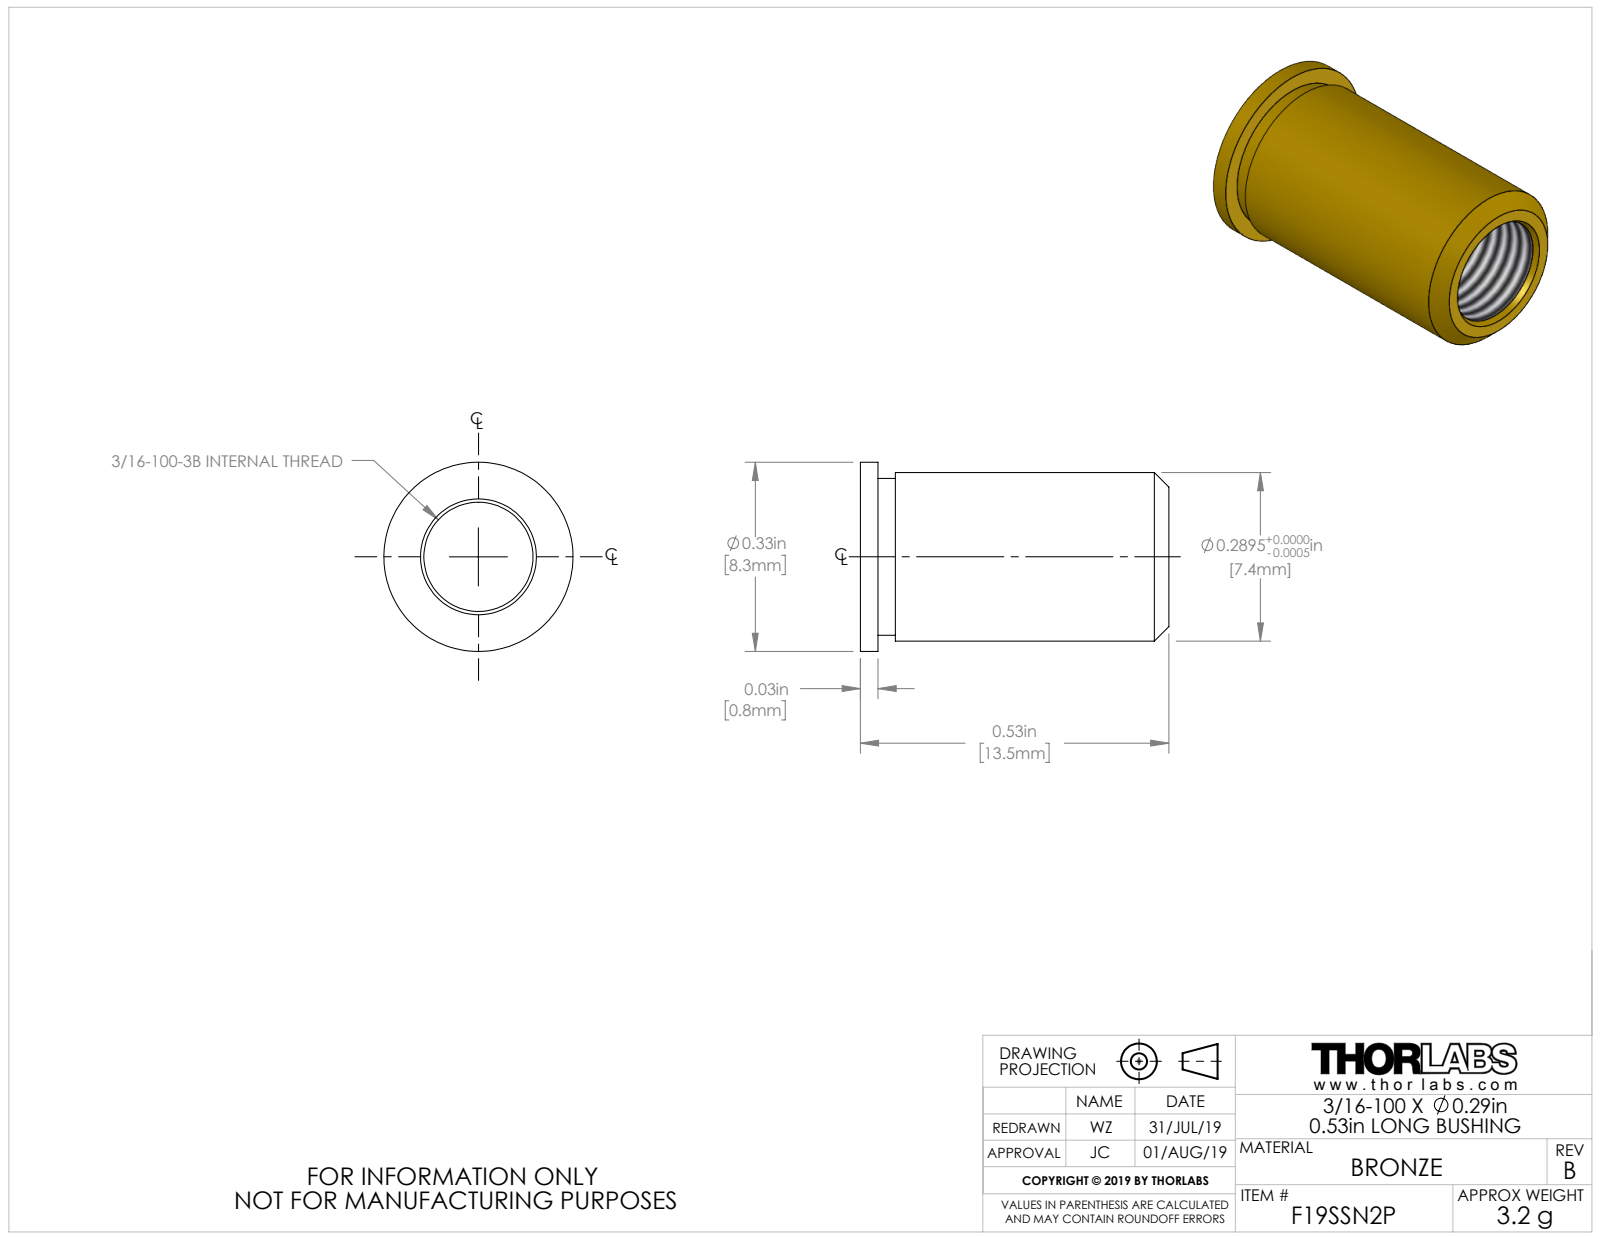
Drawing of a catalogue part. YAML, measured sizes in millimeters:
part_name: "18989-E0W"
step_written_by: "SolidWorks 2007 (AUTOMOTIVE_DESIGN)"
units: millimeters
bodies: {solids: 1, faces: 18, planar: 4, cylindrical: 8, other: 6}
overall_size: [13.46, 8.26, 8.26]
volume: 331
surface_area: 584
round_holes:
  - {diameter: 4.76, count: 1}
round_bosses_or_shafts:
  - {diameter: 8.25, count: 1}
  - {diameter: 7.35, count: 1}
  - {diameter: 6.85, count: 1}
face_to_face_distances: [0.76, 13.46, 12.7, 1.52, 11.94]
